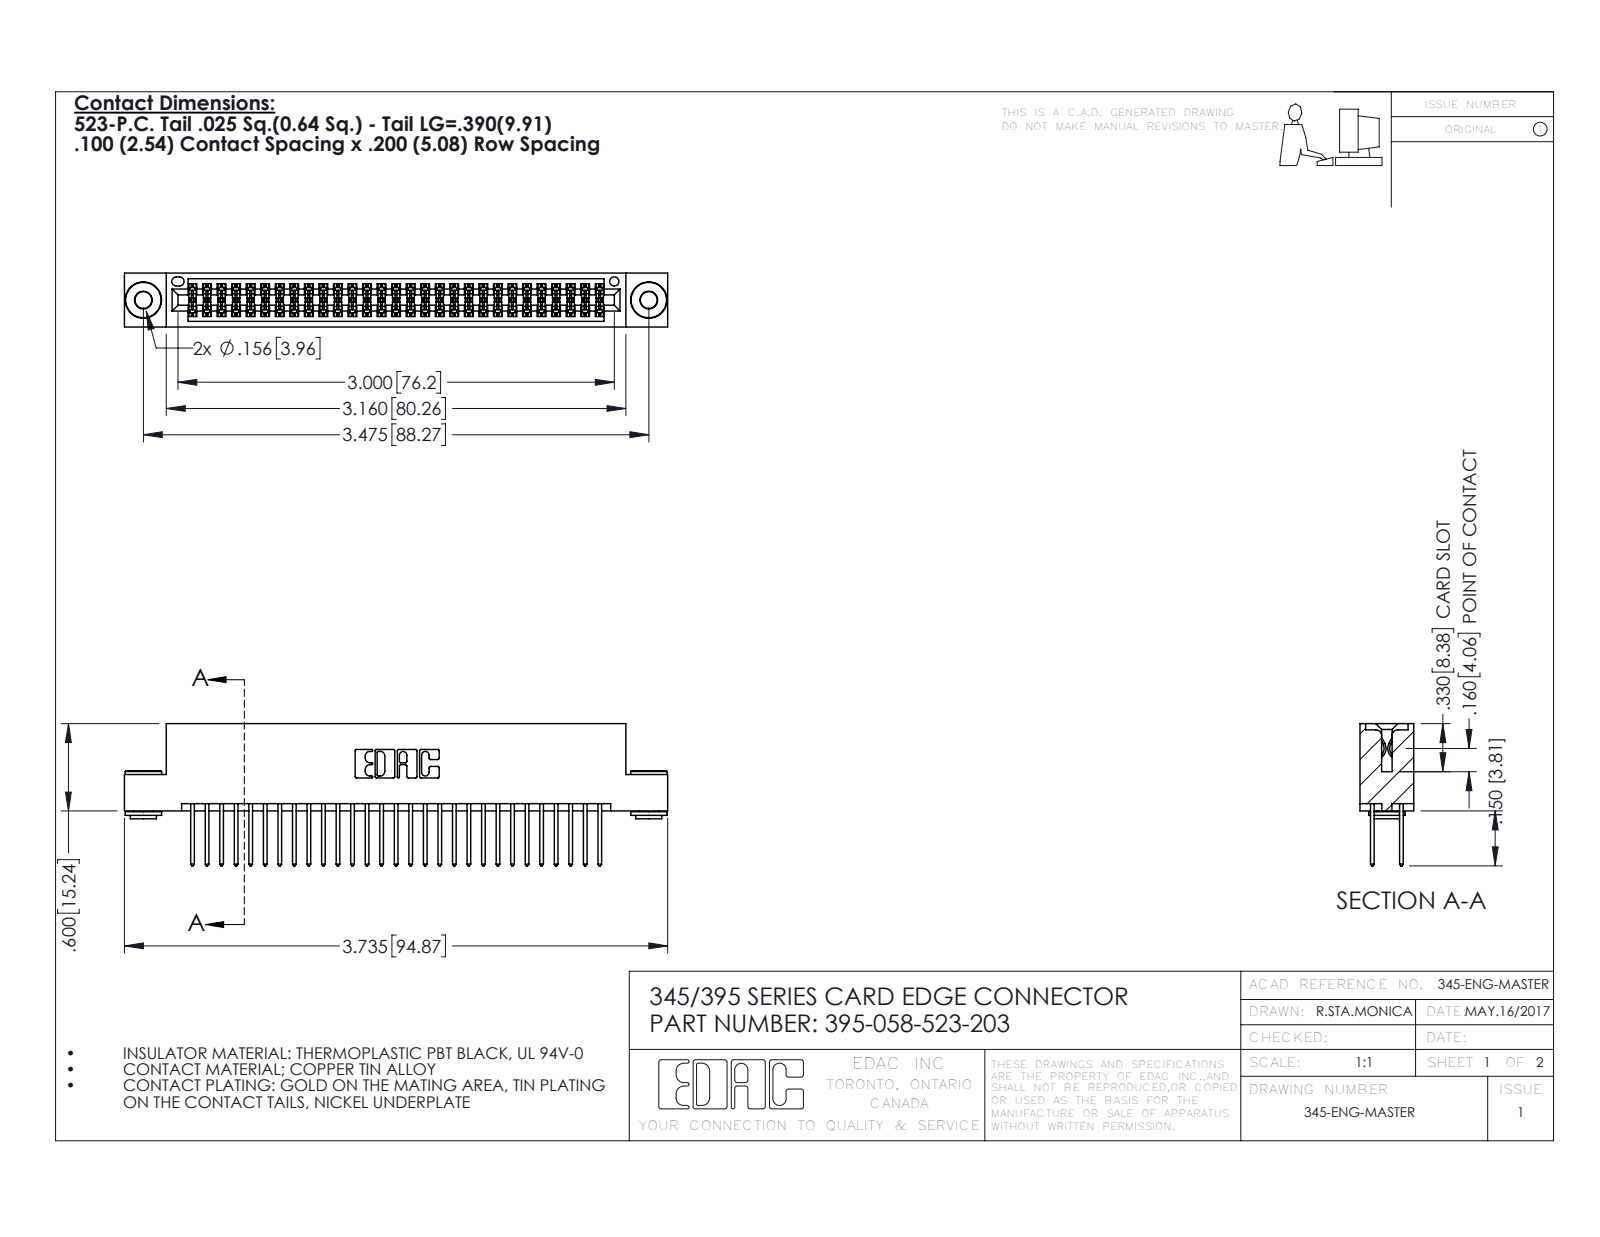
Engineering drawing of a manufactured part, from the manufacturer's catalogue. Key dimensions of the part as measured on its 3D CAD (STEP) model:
Part name (STEP PRODUCT): 395-058-523-203; 345 Part_Flush Mounting Lugs - 0.156 Dia-TH; 345-292-001_345-293-123; 345-250-002_345-250-002-102
STEP written by: SolidWorks 2016 (CONFIG_CONTROL_DESIGN)
Units: inches
Bodies: 61 solids, 3064 faces (2004 planar, 1052 cylindrical, 8 other)
Overall size (bounding box): 3.735 × 0.977 × 0.37
Volume: 0.563 in³ · Surface area: 21.91 in²
Round holes (diameter × count): ⌀0.116 ×2, ⌀0.156 ×2, ⌀0.064 ×1
Round bosses / shafts (diameter × count): ⌀0.25 ×2, ⌀0.18 ×2, ⌀0.136 ×2
Partial cylindrical surfaces — rounded edges, fillets, slot ends (radius × count): R0.006 ×87, R0.01 ×58, R0.01 ×22, R0.007 ×6, R0.031 ×6, R0.026 ×3, R0.014 ×2, R0.019 ×2
Main face-to-face distances: 0.072, 0.298, 0.2, 0.025, 0.098, 0.272, 0.37, 0.225, 0.175, 0.149
Hole centre spacings: 0.27, 3.24, 3.475
